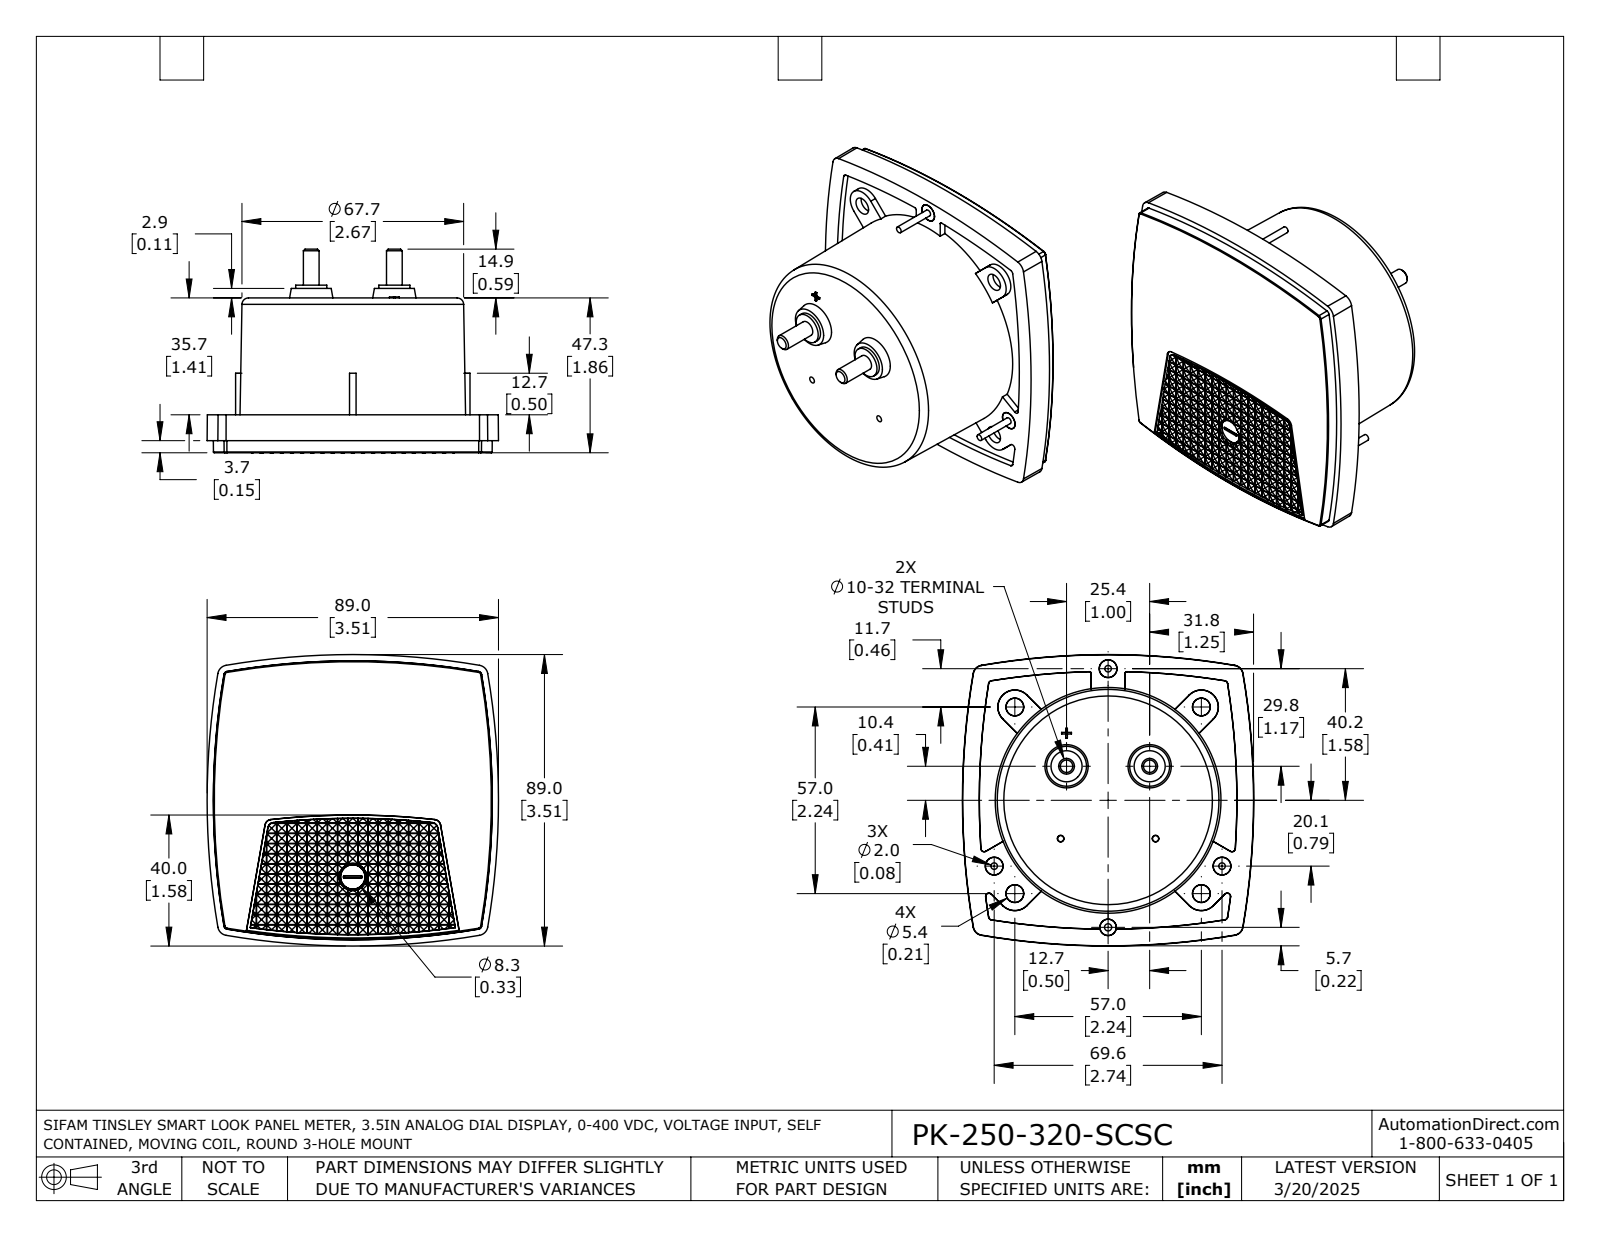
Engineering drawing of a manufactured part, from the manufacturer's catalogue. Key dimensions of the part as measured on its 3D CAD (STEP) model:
Part name (STEP PRODUCT): PK-250-320-SCSC
STEP written by: SolidWorks 2021 (AUTOMOTIVE_DESIGN)
Units: inches
Bodies: 1 solid, 1078 faces (950 planar, 23 cylindrical, 105 other)
Overall size (bounding box): 3.505 × 3.505 × 2.453
Volume: 12.99 in³ · Surface area: 44.29 in²
Round holes (diameter × count): ⌀0.087 ×1
Round bosses / shafts (diameter × count): ⌀0.213 ×3, ⌀0.079 ×3, ⌀0.374 ×2, ⌀0.189 ×2
Partial cylindrical surfaces — rounded edges, fillets, slot ends (radius × count): R8.961 ×1
Main face-to-face distances: 1.862, 1.406, 0.457, 0.079, 1.484, 0.378, 0.024, 0.096, 0.072, 0.12
